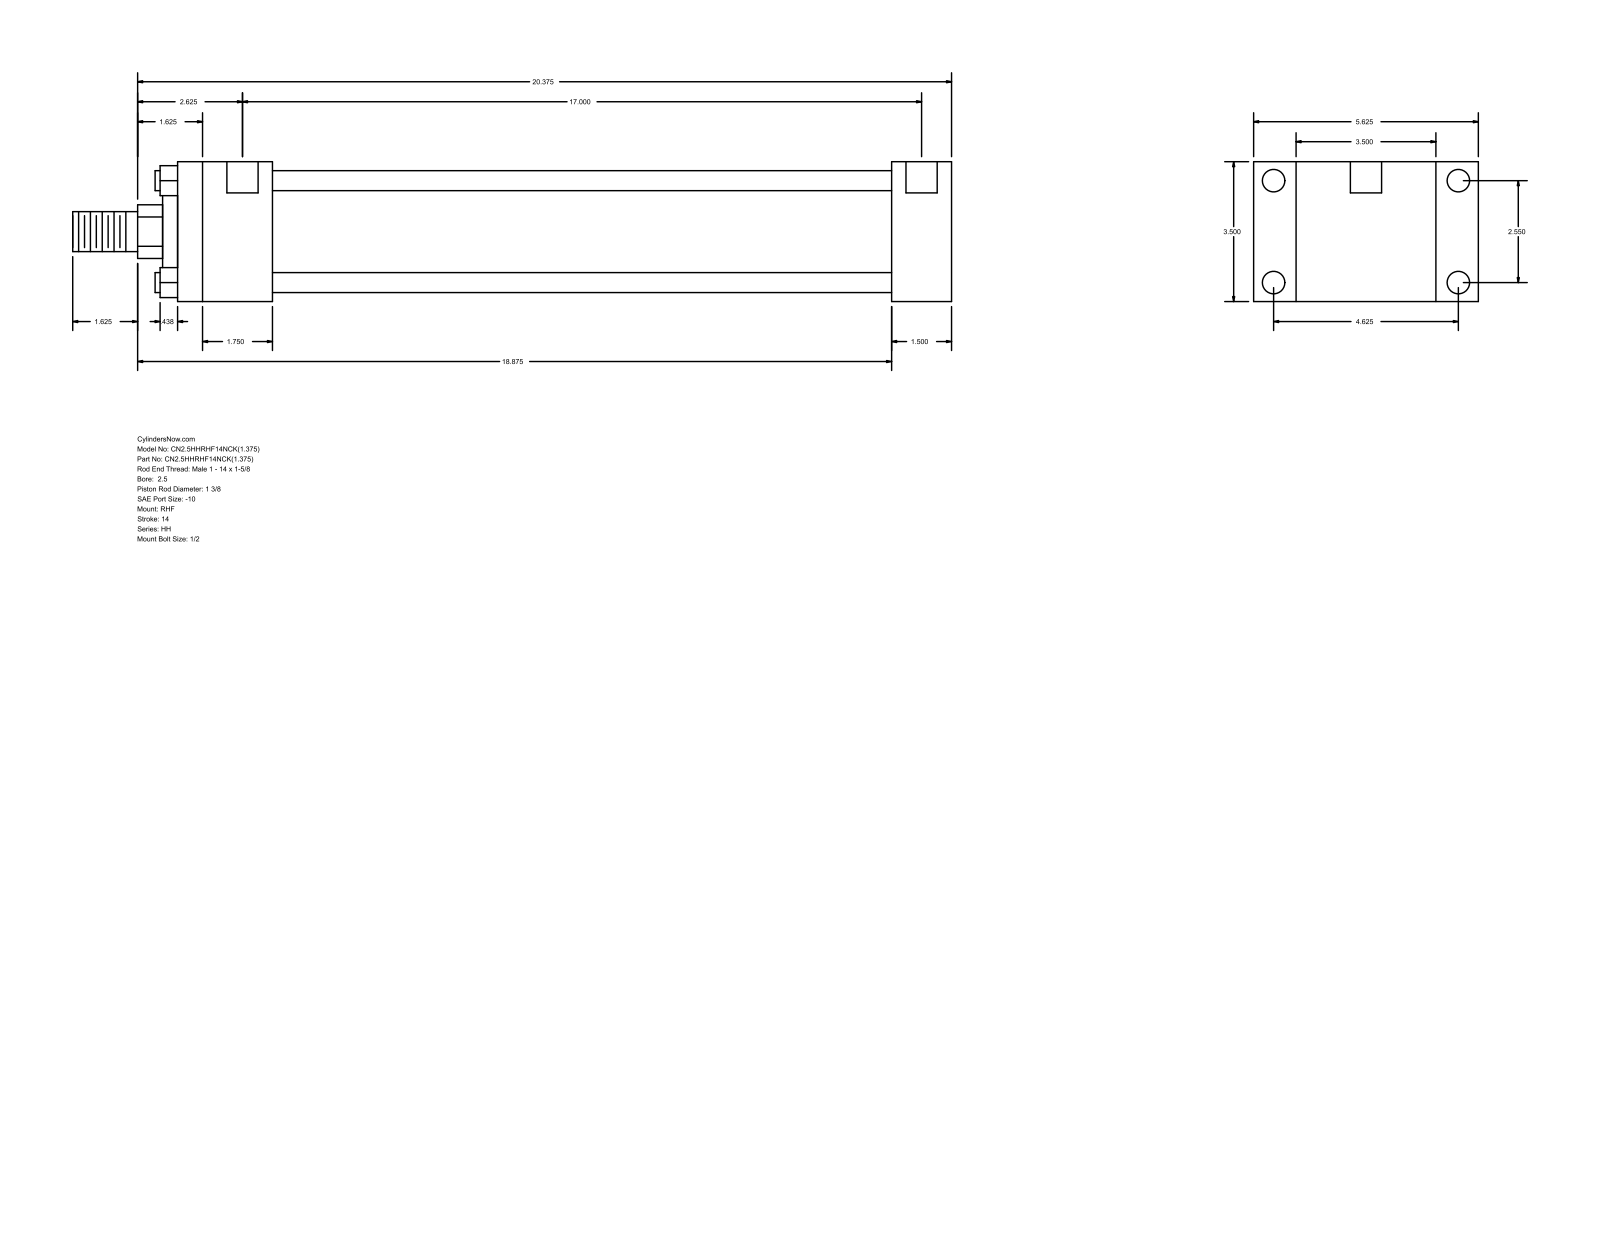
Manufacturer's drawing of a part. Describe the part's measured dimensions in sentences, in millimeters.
The part is named "HH_RHF__0250_1.375". Its 3-D file was written by "GSSL Pune (CONFIG_CONTROL_DESIGN)". It is 0 solids with 88 faces: 60 planar, 28 cylindrical and 0 other. Overall it measures 558.8 by 142.88 by 88.9 millimeters. Round holes: 4 of diameter 5.56, 4 of diameter 14.3, 2 of diameter 19.84. Round bosses or shafts: 4 of diameter 12.7, 1 of diameter 73.03, 1 of diameter 50.8, 1 of diameter 34.92, 1 of diameter 25.4. Partial cylindrical surfaces (rounded edges, fillets, slot ends): 1 of radius 17.06. The main face-to-face distances are 88.9, 38.09, 26.99, 115.89, 454.03, 492.12, 142.88, 60.32, 393.71, 431.8. The hole center spacings are 1.58, 64.76, 117.48, 134.15, 433.39, 434.97, 431.81.
